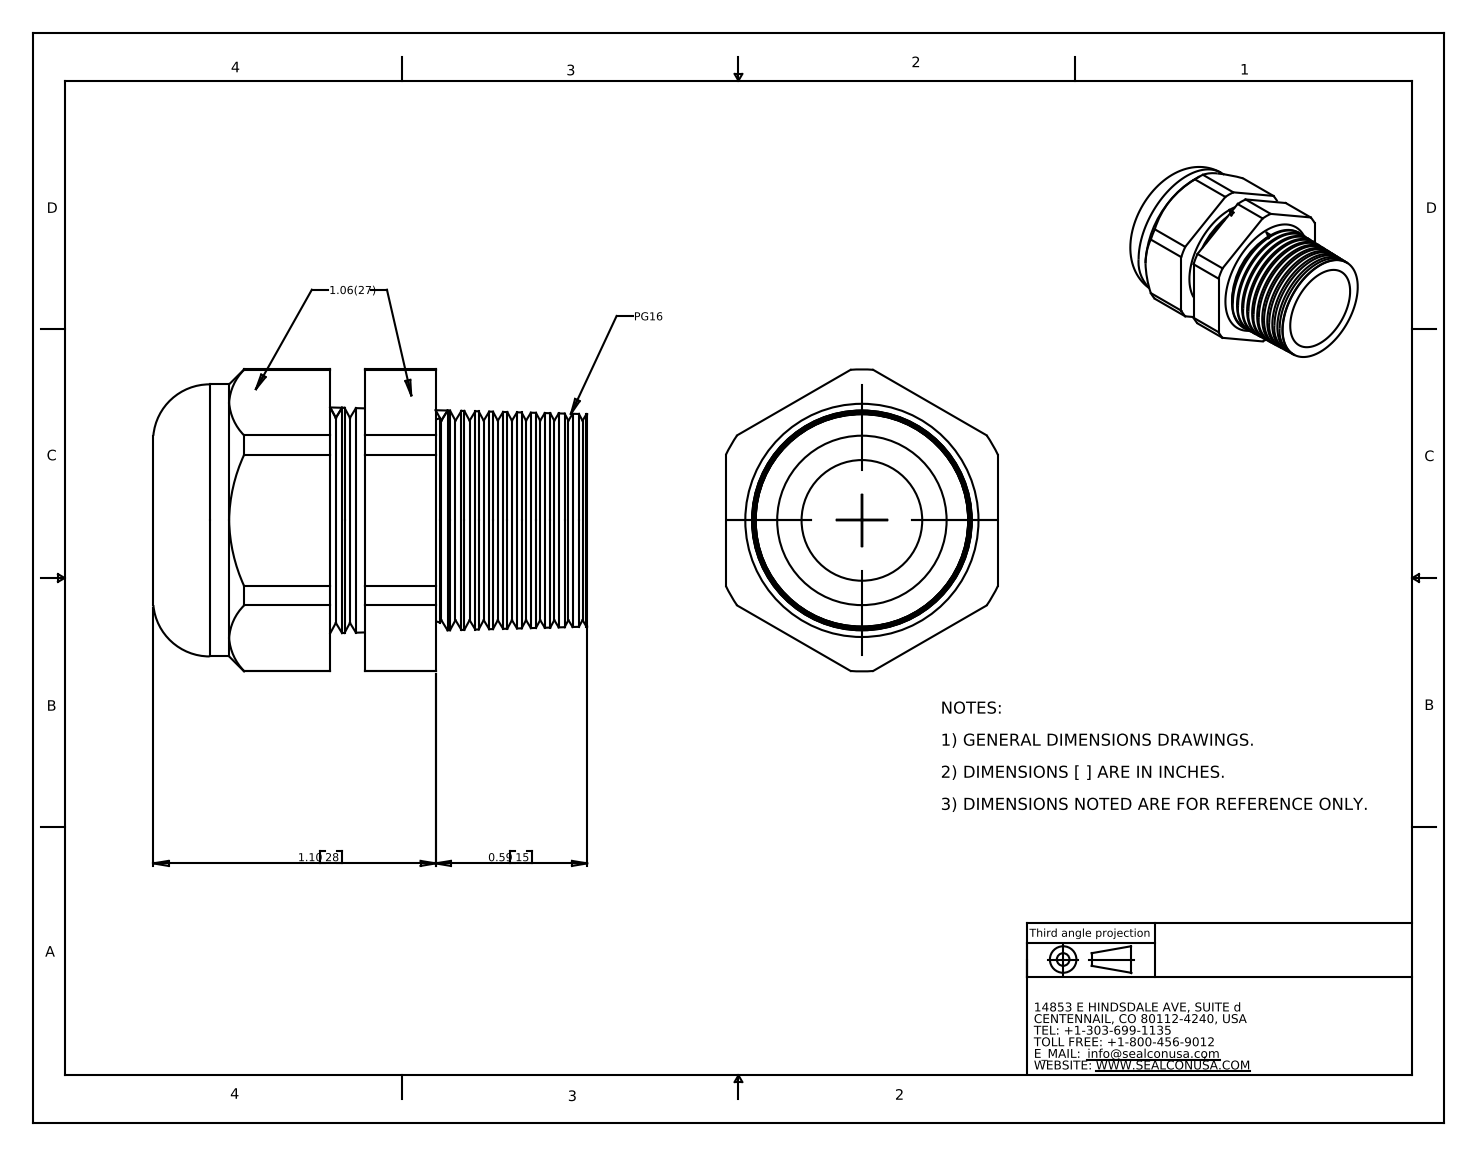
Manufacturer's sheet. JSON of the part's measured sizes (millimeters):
{"part_name": "CD16CR-GY", "step_written_by": "SolidWorks 2007 (CONFIG_CONTROL_DESIGN)", "units": "millimeters", "bodies": {"solids": 2, "faces": 135, "planar": 19, "cylindrical": 22, "other": 94}, "overall_size": [42.9, 29.9, 26.9], "volume_mm3": 14400, "surface_area_mm2": 8168, "round_holes": [[11.9, 1], [16.8, 1]], "round_bosses_or_shafts": [[26.9, 1]], "partial_cylinders_radius": [[14.9, 1]], "face_to_face_distances": [26.9, 3.4, 10, 13.4, 20.4, 10.4, 7, 35.4, 25.4, 22]}
